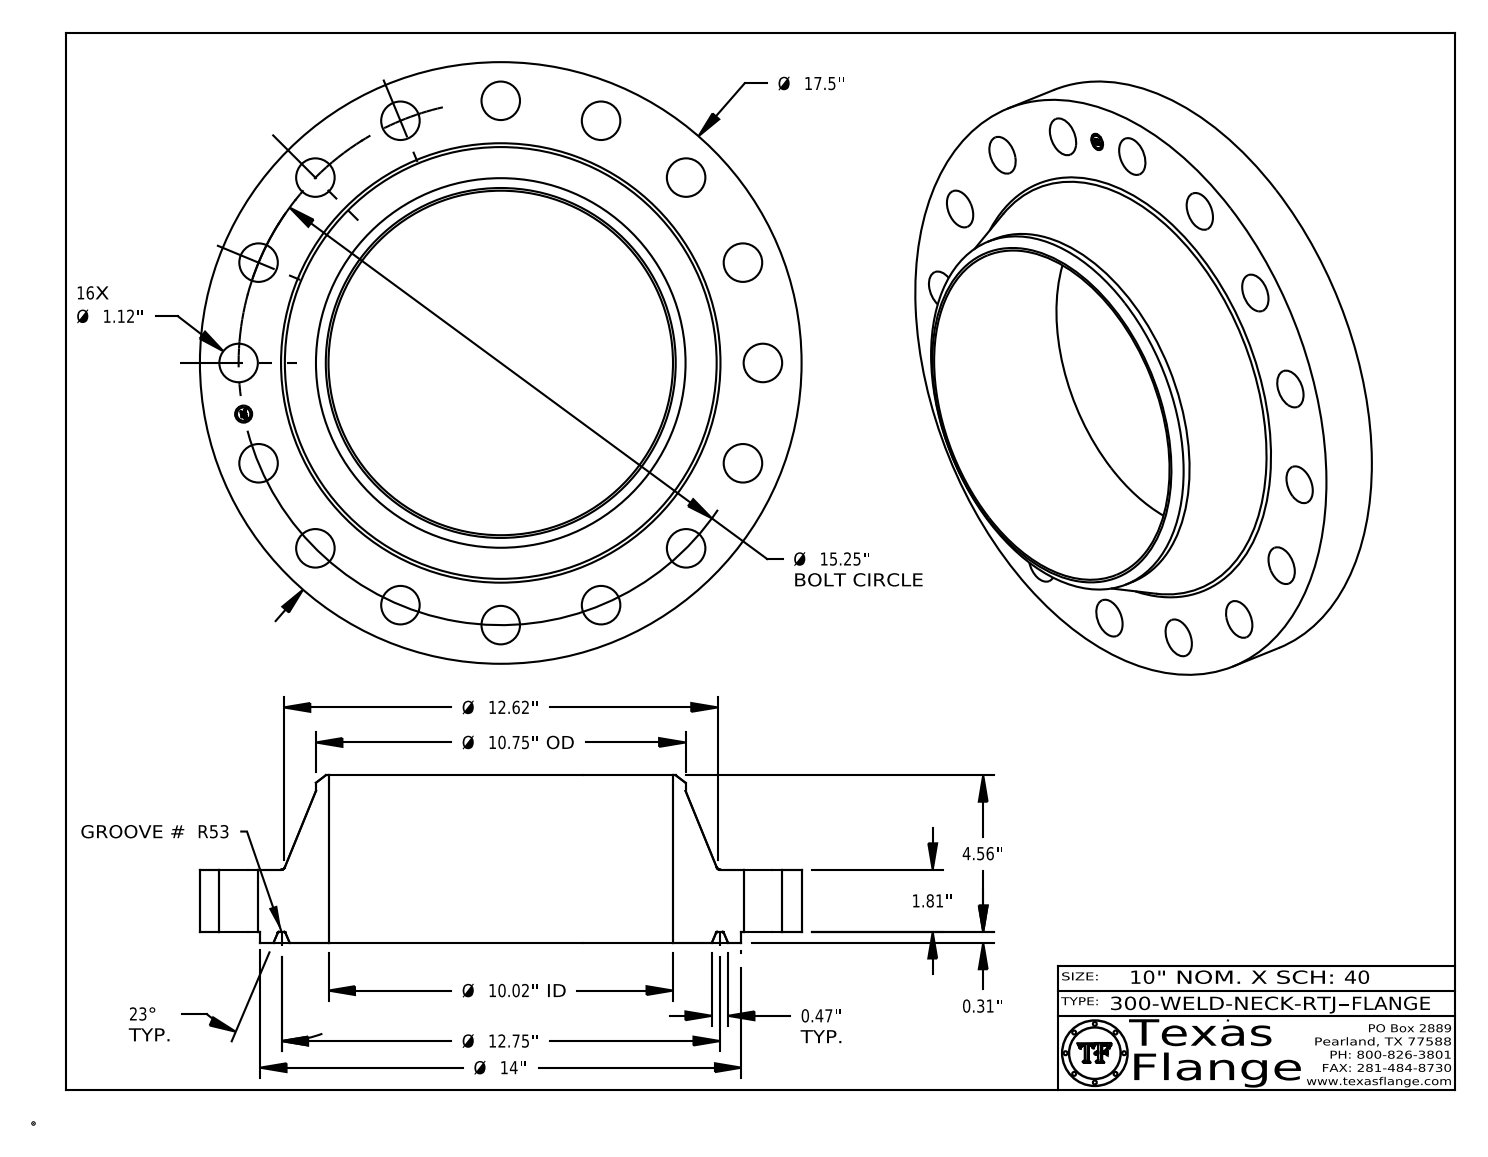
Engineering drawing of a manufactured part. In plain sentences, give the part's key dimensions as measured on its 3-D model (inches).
The part is named "300-WELD-NECK-RTJ". Its 3-D file was written by "CATIA V5 STEP AP214 (AUTOMOTIVE_DESIGN)". It is 1 solid with 445 faces: 371 planar, 60 cylindrical and 14 other. Overall it measures 17.5 by 17.5 by 4.873 inches. Its volume is 353.5 cubic inches and its surface area 743 square inches. Round holes: 16 of diameter 1.12, 1 of diameter 0.495, 1 of diameter 10.02. Round bosses or shafts: 8 of diameter 0.03, 1 of diameter 17.5, 1 of diameter 14, 1 of diameter 10.75, 1 of diameter 0.39. The main face-to-face distances are 1.81, 0.313, 2.123, 4.873, 4.56, 2.75, 0.015, 2.108, 1.795, 2.765. The hole center spacings are 8.472, 10.783, 14.957, 14.089, 7.625, 2.975, 2.975, 5.836.
